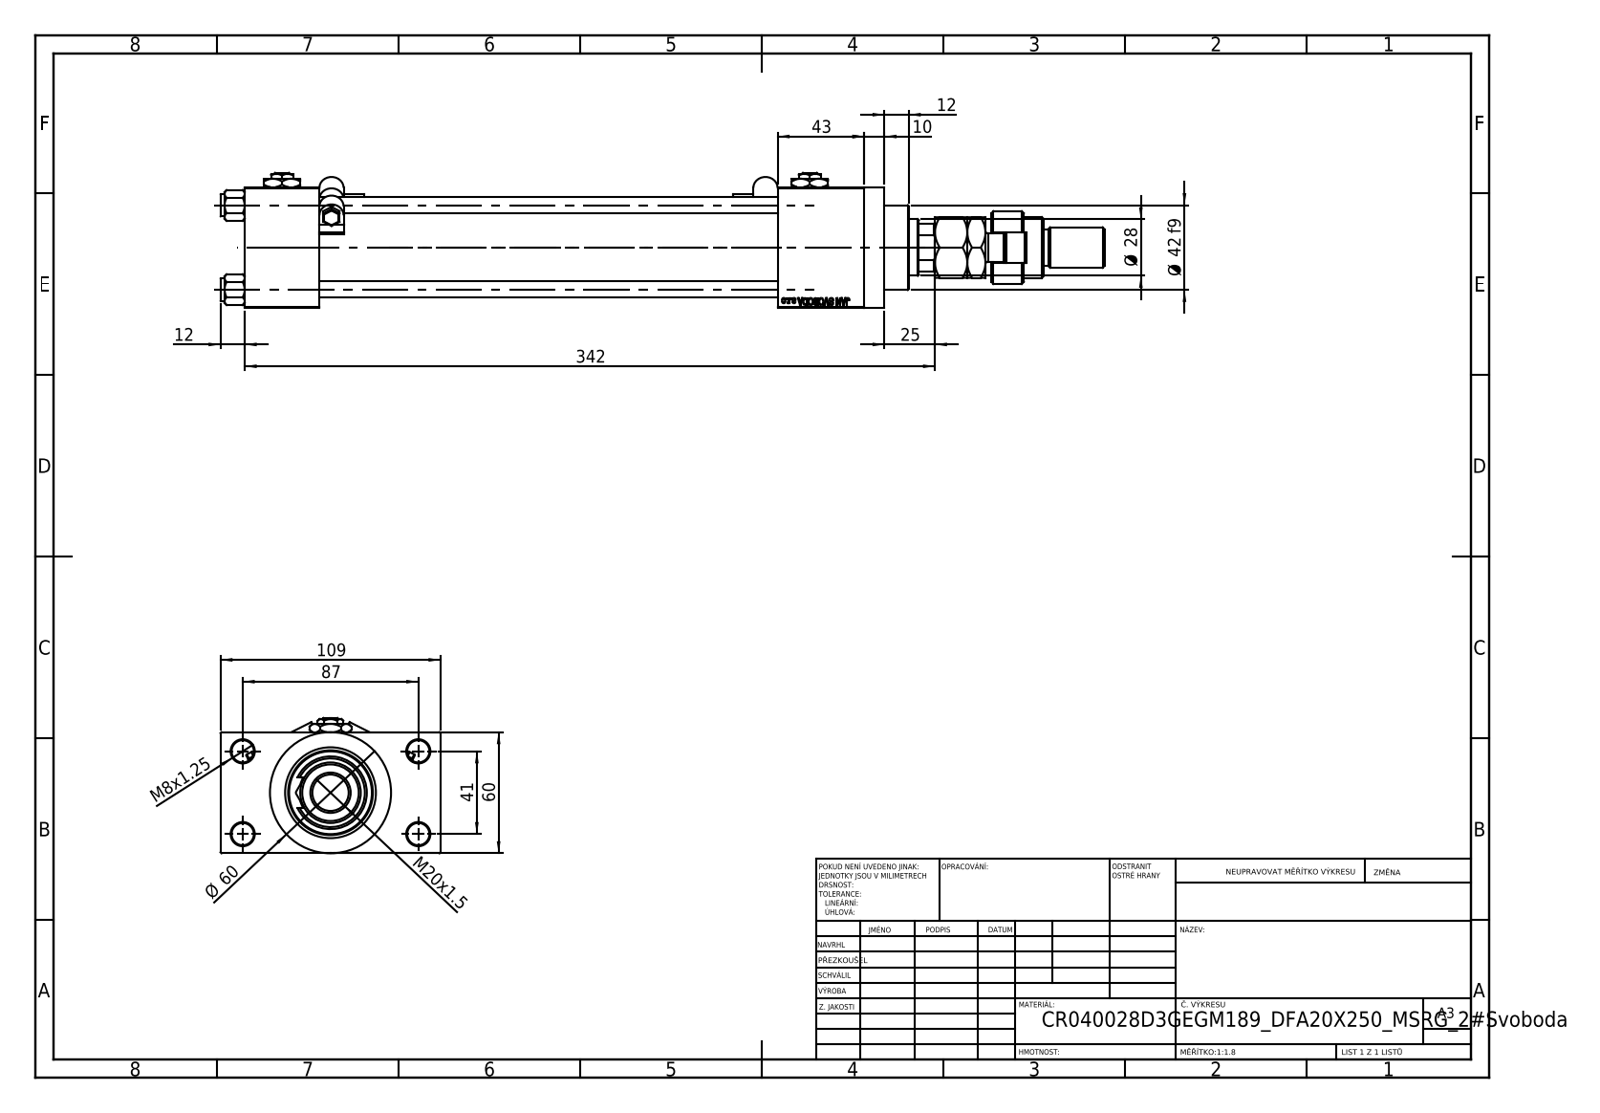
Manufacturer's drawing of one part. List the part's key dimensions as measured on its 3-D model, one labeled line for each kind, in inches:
Part name (STEP PRODUCT): NUT_M5_D; V215CR_D_TYCINKA; Zatka_pro_OIL_PORT; V215CR_VCP_D (+5 more)
STEP written by: SolidWorks 2019 (CONFIG_CONTROL_DESIGN)
Units: inches
Bodies: 17 solids, 1355 faces (610 planar, 141 cylindrical, 604 other)
Overall size (bounding box): 17.244 × 4.291 × 2.638
Volume: 48.48 in³ · Surface area: 349.6 in²
Round holes (diameter × count): ⌀0.315 ×4, ⌀0.433 ×4, ⌀0.276 ×2, ⌀0.656 ×2, ⌀0.945 ×2, ⌀0.728 ×1, ⌀1.102 ×1, ⌀1.22 ×1, ⌀1.575 ×1, ⌀1.772 ×1
Round bosses / shafts (diameter × count): ⌀0.433 ×4, ⌀0.197 ×2, ⌀0.098 ×2, ⌀2.362 ×1, ⌀1.811 ×1, ⌀1.654 ×1, ⌀1.417 ×1, ⌀1.181 ×1
Partial cylindrical surfaces — rounded edges, fillets, slot ends (radius × count): R0.02 ×12, R0.236 ×4, R0.295 ×1, R0.472 ×1, R0.531 ×1
Main face-to-face distances: 2.362, 0.965, 3.327, 8.937, 1.457, 10.394, 1.693, 12.087, 10.63, 4.291
Hole centre spacings: 0.892, 1.161, 1.642, 1.856, 1.893, 2.533, 3.011, 1.614
